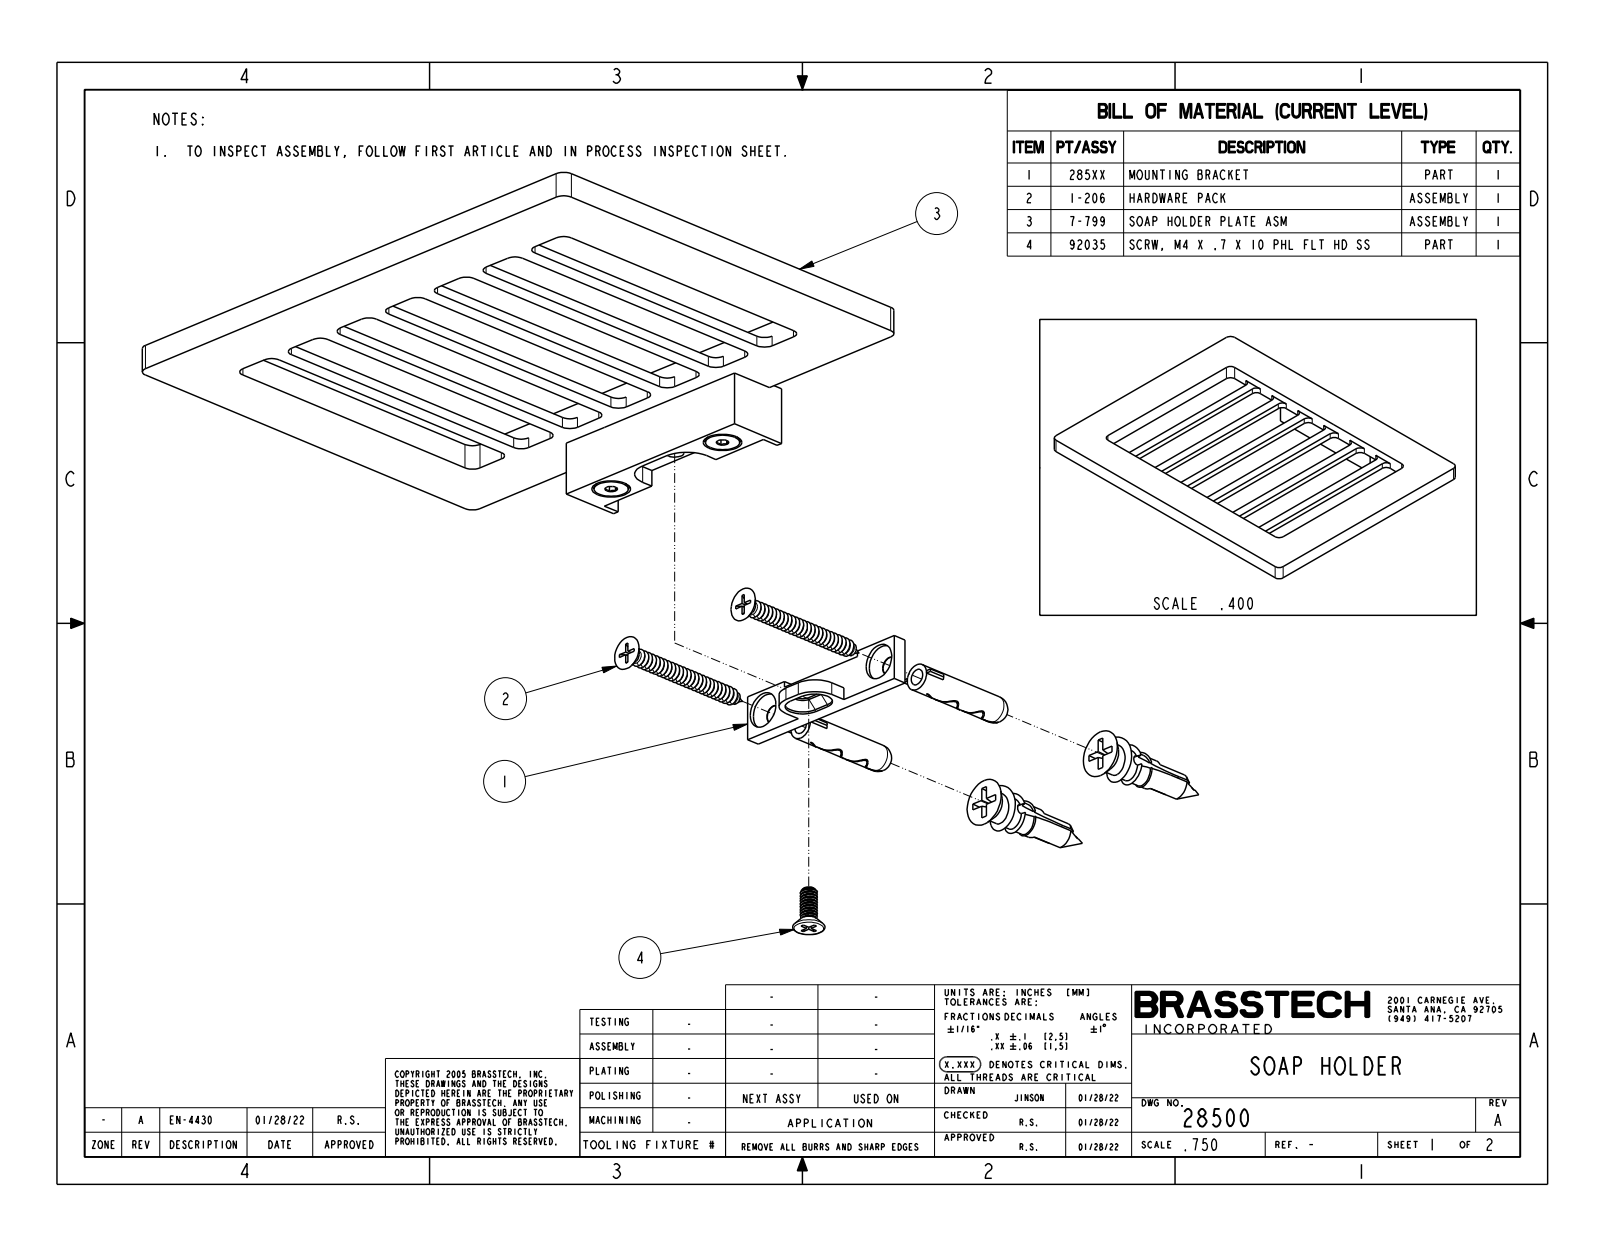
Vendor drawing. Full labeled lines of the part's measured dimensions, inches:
Part name (STEP PRODUCT): 28500_SW0003
STEP written by: CREO PARAMETRIC BY PTC INC, 2025093 (CONFIG_CONTROL_DESIGN)
Units: inches
Bodies: 1 solid, 66 faces (34 planar, 32 cylindrical, 0 other)
Overall size (bounding box): 5.512 × 4.489 × 0.748
Volume: 3.536 in³ · Surface area: 42.45 in²
Partial cylindrical surfaces — rounded edges, fillets, slot ends (radius × count): R0.098 ×32
Main face-to-face distances: 0.236, 0.63, 0.098, 0.138, 0.158, 1.26, 2.52, 1.102, 3.15, 1.89
